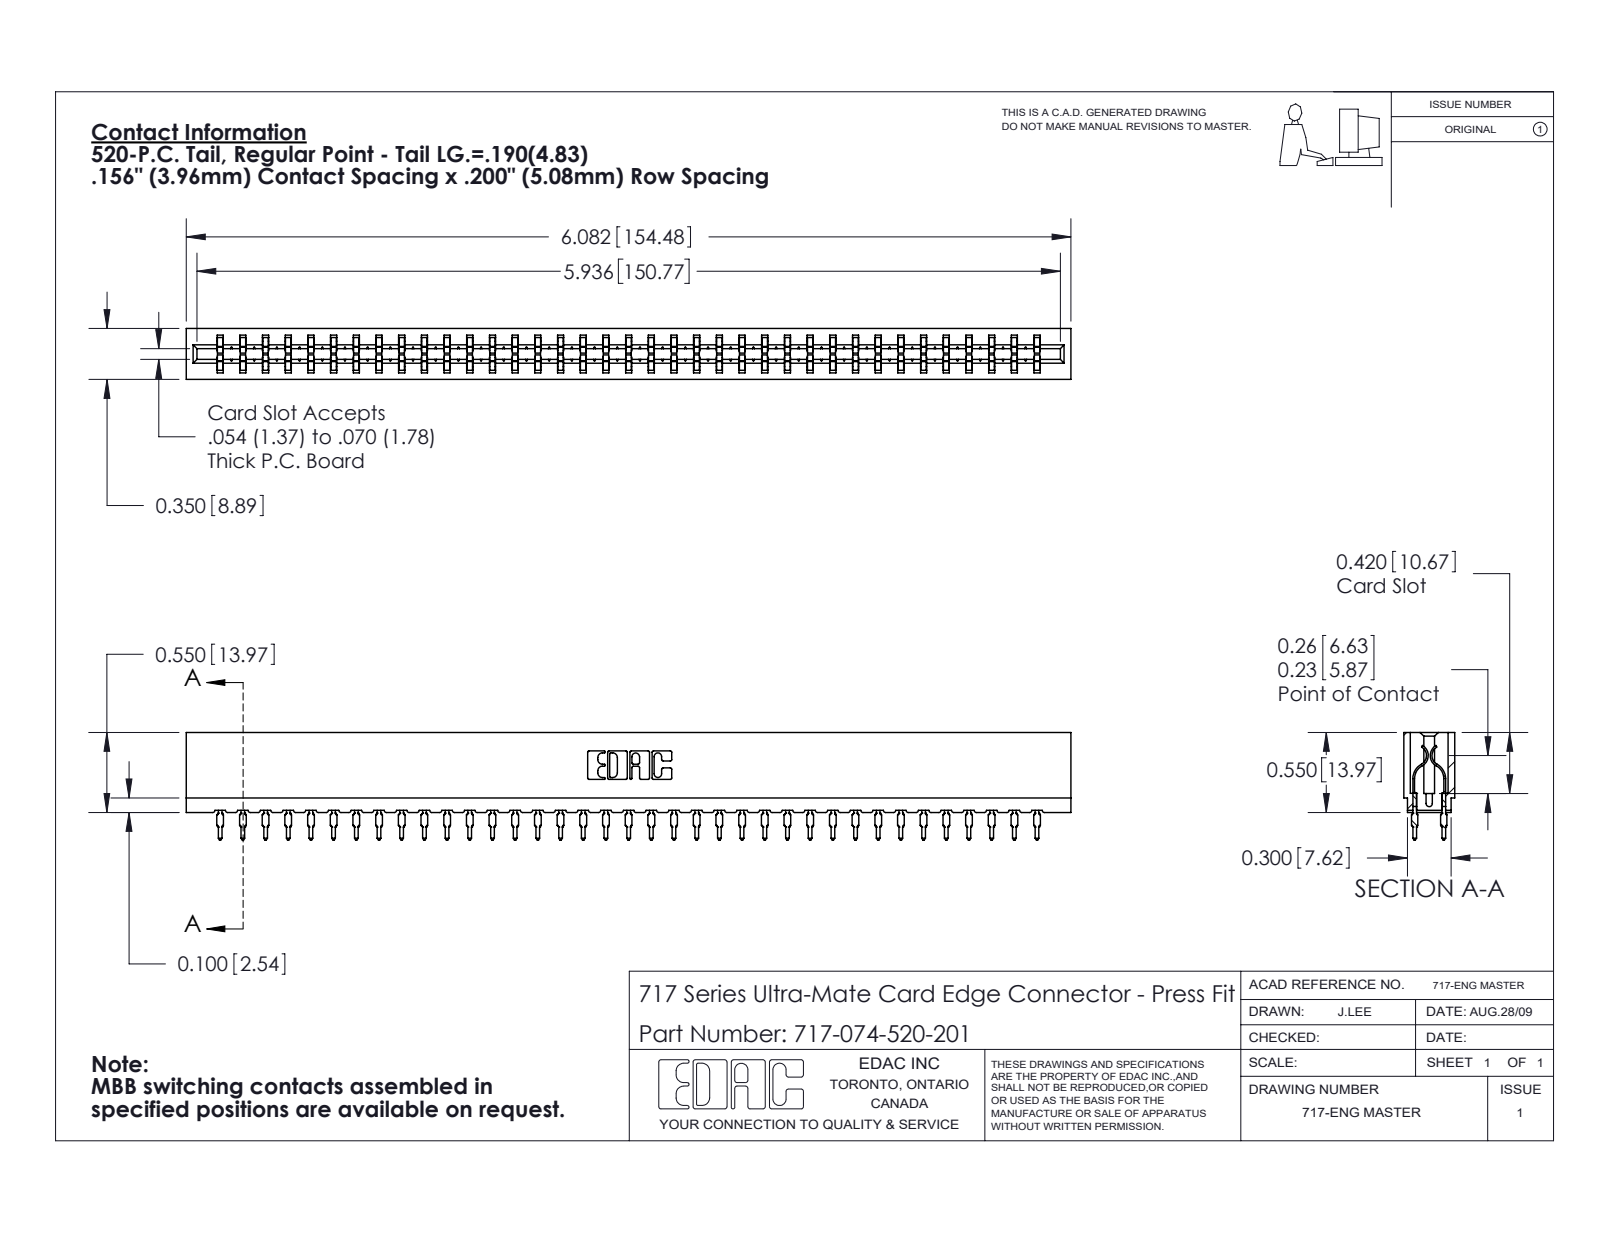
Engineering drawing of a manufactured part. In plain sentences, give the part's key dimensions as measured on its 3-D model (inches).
The part is named "745-292-001_520; 717-074-520-201; 717 Part_Insulator Option - 06". Its 3-D file was written by "SolidWorks 2020 (CONFIG_CONTROL_DESIGN)". It is 75 solids with 6754 faces: 3495 planar, 1335 cylindrical and 1924 other. Overall it measures 6.082 by 0.739 by 0.35 inches. Its volume is 0.814 cubic inches and its surface area 30.95 square inches. Partial cylindrical surfaces (rounded edges, fillets, slot ends): 148 of radius 0.021, 74 of radius 0.015, 22 of radius 0.01, 8 of radius 0.005, 8 of radius 0.011, 6 of radius 0.007, 6 of radius 0.031, 3 of radius 0.026. The main face-to-face distances are 0.212, 0.138, 0.35, 0.063, 0.287, 0.076, 0.149, 0.074, 0.045, 0.305.
